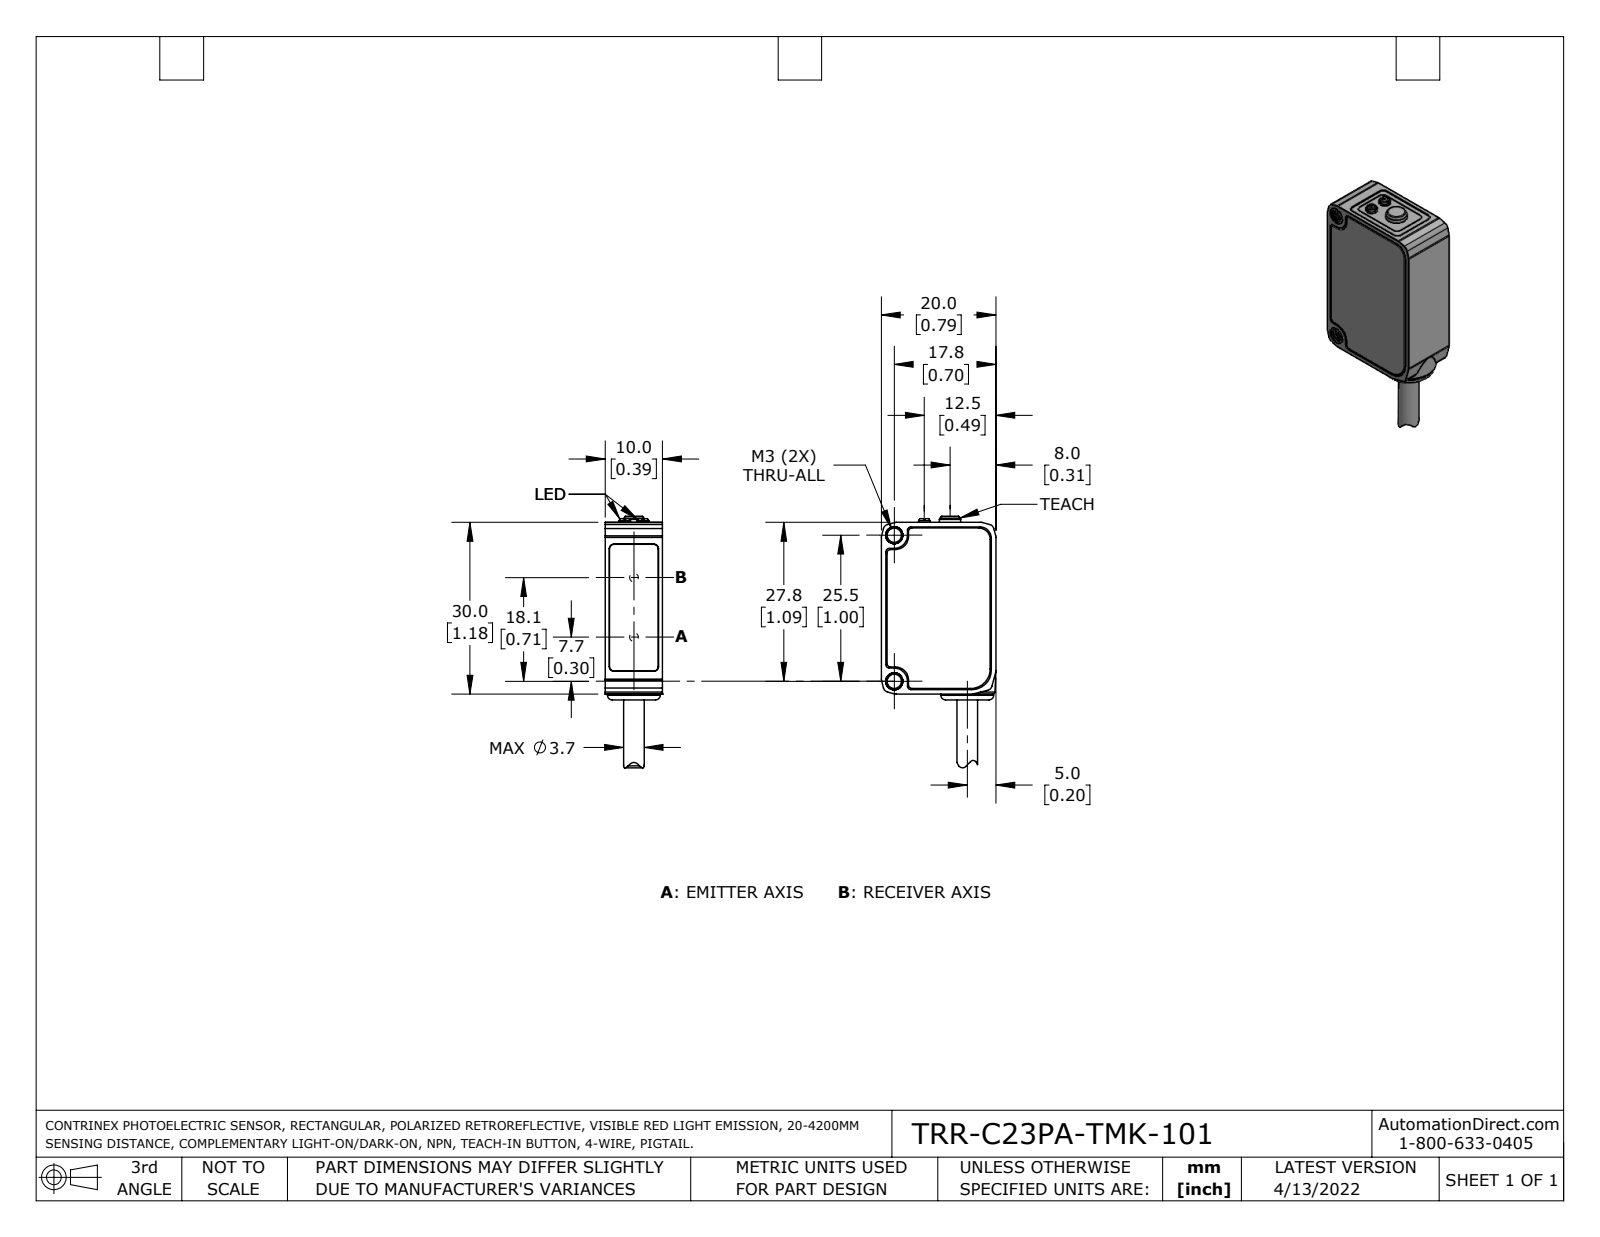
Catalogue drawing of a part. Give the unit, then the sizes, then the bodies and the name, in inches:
Units: inches
Overall size (bounding box): 1.728 × 0.787 × 0.394
Round holes (diameter × count): ⌀0.098 ×2, ⌀0.142 ×2
Round bosses / shafts (diameter × count): ⌀0.079 ×2, ⌀0.362 ×1, ⌀0.146 ×1, ⌀0.142 ×1
Partial cylindrical surfaces — rounded edges, fillets, slot ends (radius × count): R0.031 ×20, R0.039 ×11, R0.024 ×8, R0.091 ×4, R0.134 ×3, R0.079 ×2, R0.025 ×1, R0.033 ×1
Main face-to-face distances: 0.394, 0.785, 0.039, 0.787, 1.181, 1.177, 1.217, 1.22, 0.028, 1.219
Hole centre spacings: 1.004
Volume: 0.365 in³ · Surface area: 4.154 in²
Bodies: 1 solid, 269 faces (87 planar, 136 cylindrical, 46 other)
Part name (STEP PRODUCT): TRR-C23PA-TMK-101
STEP written by: SolidWorks 2021 (AUTOMOTIVE_DESIGN)
